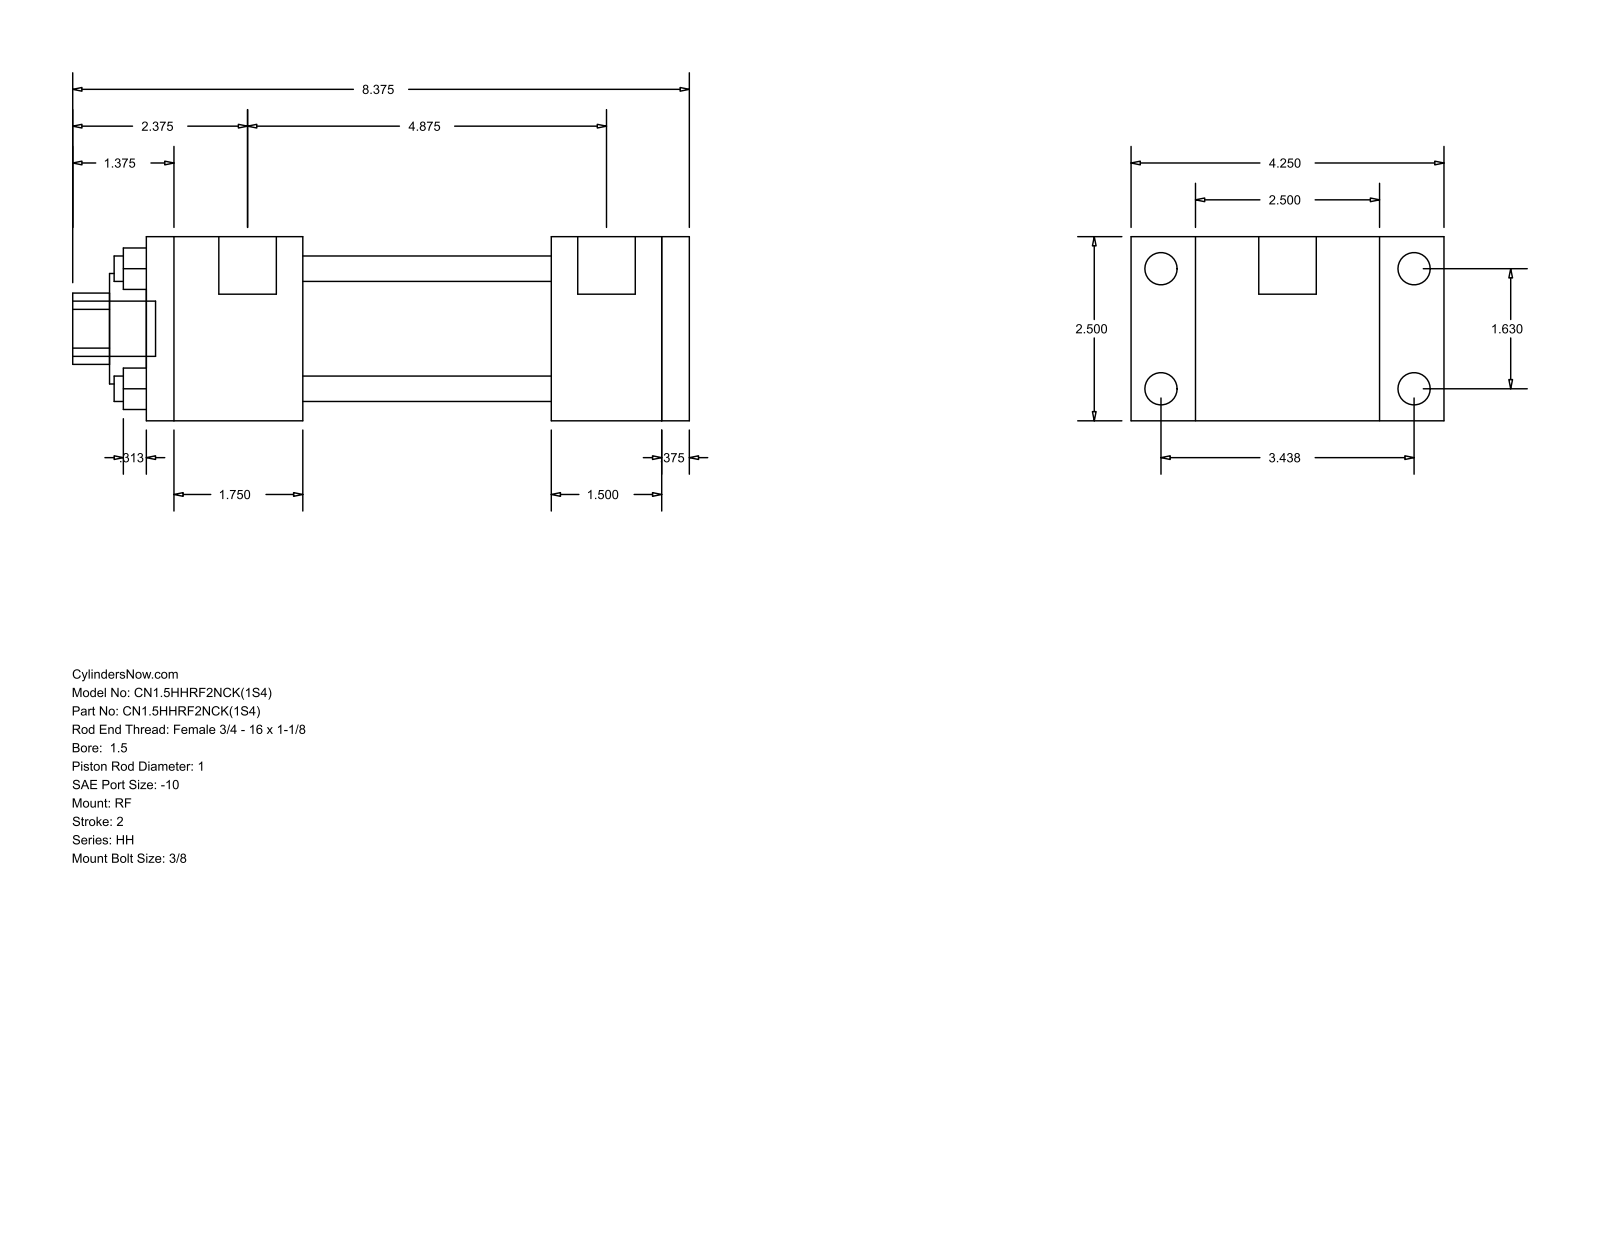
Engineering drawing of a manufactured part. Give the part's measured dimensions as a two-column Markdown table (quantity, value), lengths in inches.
| quantity | value |
| --- | --- |
| part name | HH_RF__0150_1 |
| STEP written by | GSSL Pune (CONFIG_CONTROL_DESIGN) |
| units | inches |
| bodies | 0 solids, 92 faces (64 planar, 28 cylindrical, 0 other) |
| overall size | 8.375 × 4.25 × 2.5 |
| round holes (diameter × count) | 0.345 × 4, 1 × 1, 1.5 × 1, 1.75 × 1 |
| round bosses / shafts (diameter × count) | 0.438 × 4, 0.219 × 4, 0.781 × 2, 0.75 × 1 |
| partial cylindrical surfaces (radius × count) | 0.484 × 1 |
| main face-to-face distances | 2.5, 0.375, 3.375, 4.875, 5.25, 1.5, 1.875, 2.125, 5.5, 7 |
| hole center spacings | 1.152, 1.63, 2.305 |
